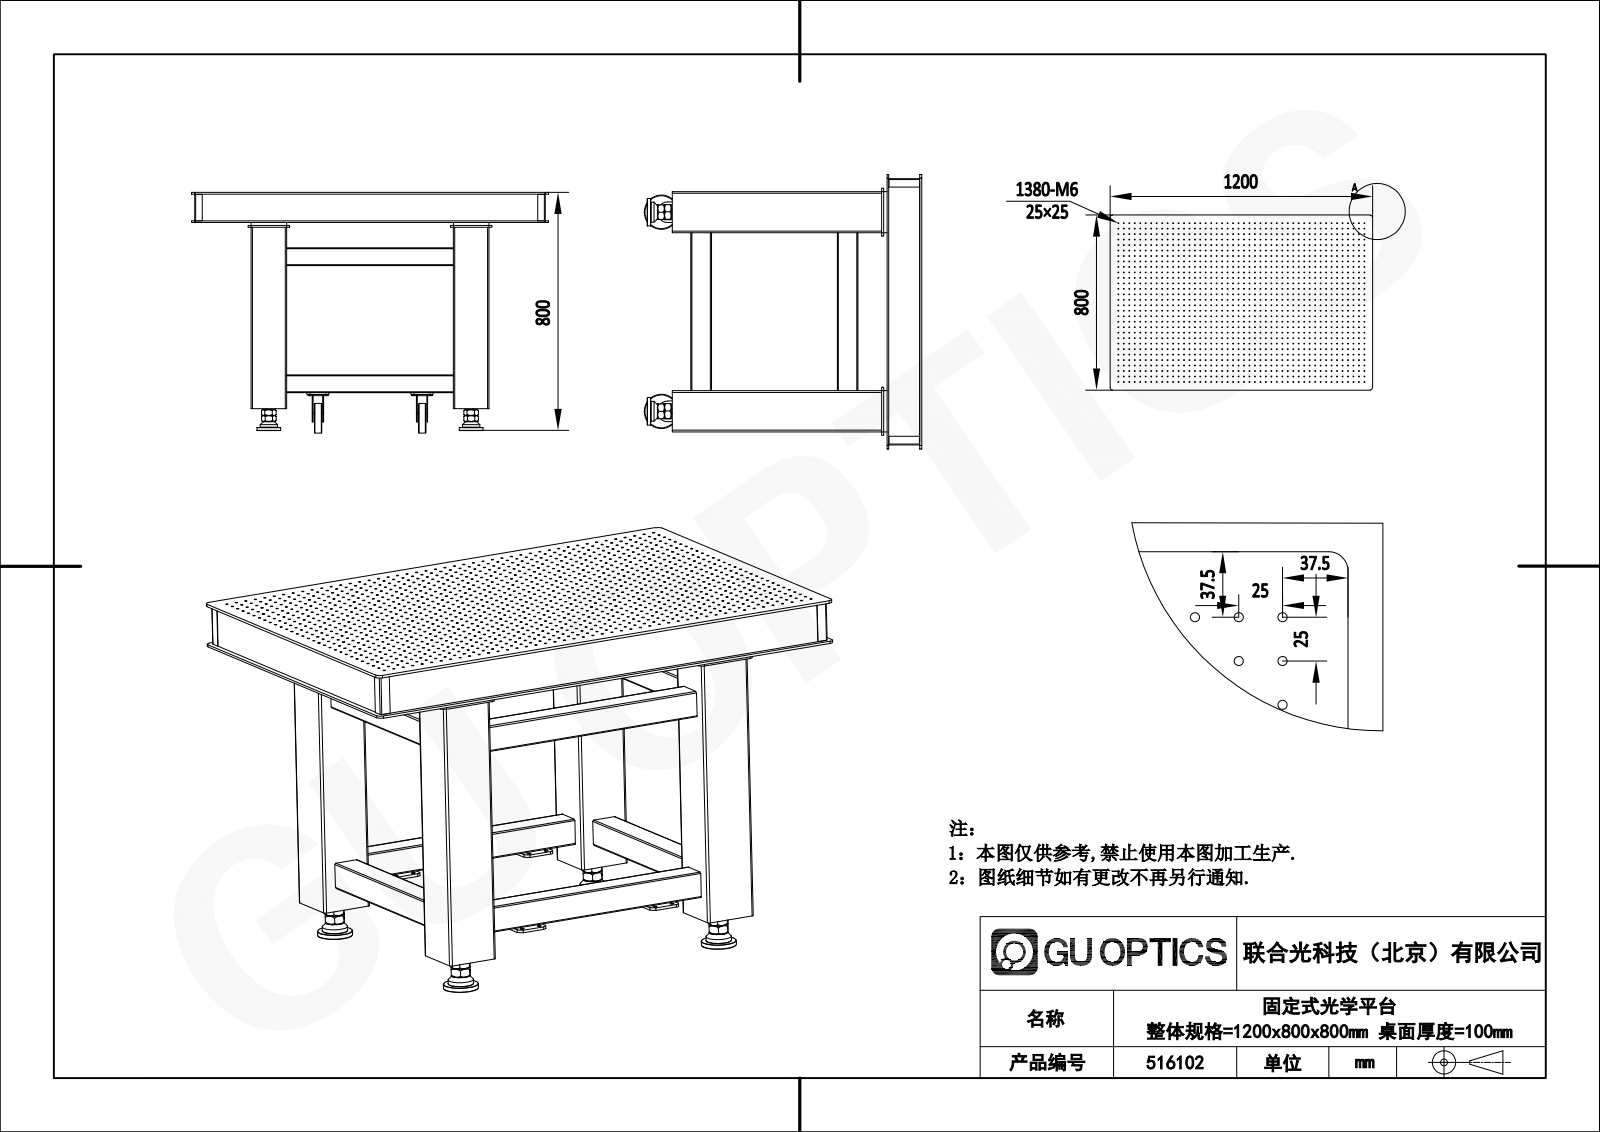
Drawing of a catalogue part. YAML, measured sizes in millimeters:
part_name: "516102"
step_written_by: "SolidWorks 2020 (AUTOMOTIVE_DESIGN)"
units: millimeters
bodies: {solids: 61, faces: 5156, planar: 1876, cylindrical: 3088, other: 192}
overall_size: [1200, 809, 800]
volume: 101500000
surface_area: 7574000
round_holes:
  - {diameter: 5.3, count: 1380}
  - {diameter: 8.5, count: 16}
  - {diameter: 9, count: 16}
  - {diameter: 17.5, count: 4}
  - {diameter: 22, count: 4}
  - {diameter: 28, count: 4}
  - {diameter: 43, count: 4}
round_bosses_or_shafts:
  - {diameter: 80, count: 4}
  - {diameter: 58, count: 4}
  - {diameter: 14, count: 4}
  - {diameter: 100, count: 2}
partial_cylinders:
  - {radius: 1, count: 48}
  - {radius: 10, count: 48}
  - {radius: 3, count: 36}
  - {radius: 5, count: 16}
  - {radius: 7, count: 16}
  - {radius: 2, count: 4}
  - {radius: 11, count: 4}
  - {radius: 30, count: 2}
face_to_face_distances: [4, 116, 101, 2, 58, 580, 680, 120, 90, 112]
hole_center_spacings: [580, 25, 45, 50, 78, 90.05, 147.74, 191.51]
